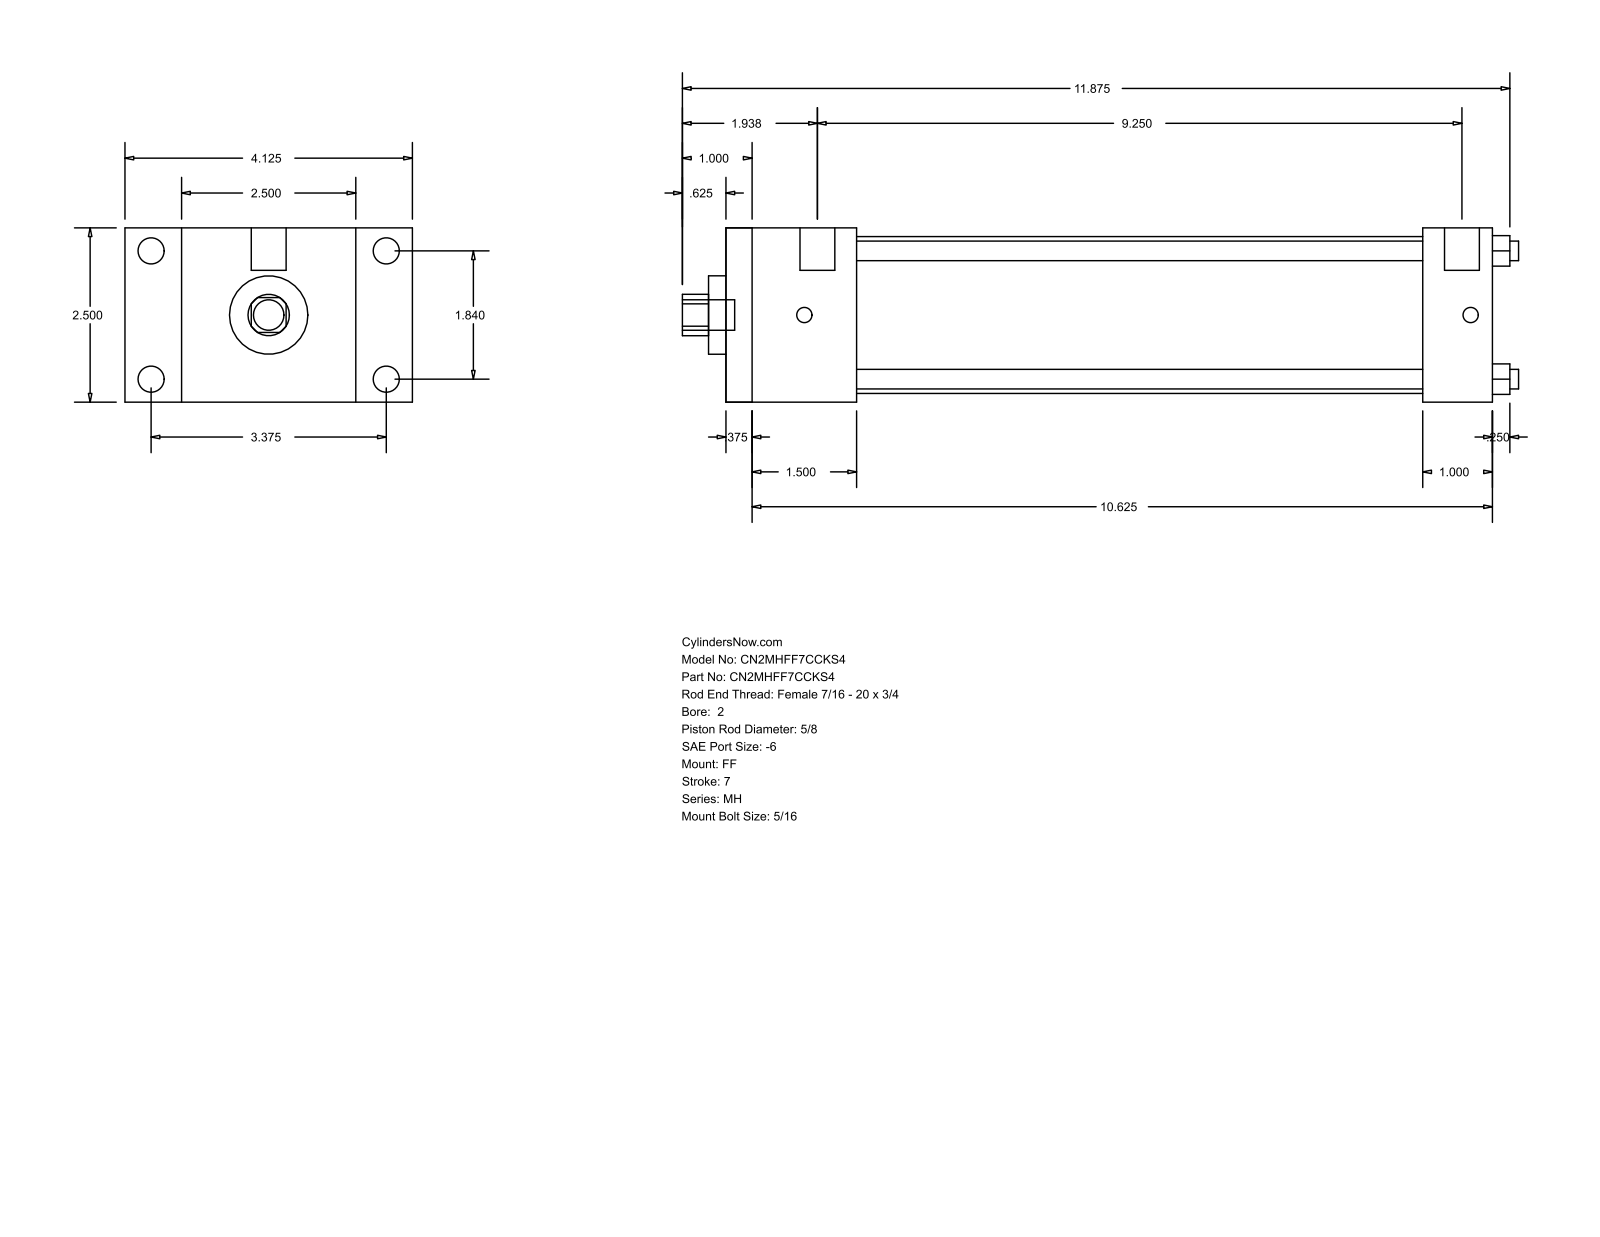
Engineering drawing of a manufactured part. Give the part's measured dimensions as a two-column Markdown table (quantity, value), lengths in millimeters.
| quantity | value |
| --- | --- |
| part name | MH_FF__0200_0.625 |
| STEP written by | GSSL Pune (CONFIG_CONTROL_DESIGN) |
| units | millimeters |
| bodies | 0 solids, 92 faces (64 planar, 28 cylindrical, 0 other) |
| overall size | 304.8 × 104.78 × 63.5 |
| round holes (diameter × count) | 7.14 × 4, 15.88 × 1, 28.57 × 1, 57.15 × 1 |
| round bosses / shafts (diameter × count) | 9.53 × 4, 5.56 × 4, 12.7 × 2, 11.11 × 1 |
| partial cylindrical surfaces (radius × count) | 7.54 × 1 |
| main face-to-face distances | 63.5, 279.39, 9.52, 269.87, 38.1, 47.62, 254, 244.48, 206.38, 231.77 |
| hole center spacings | 33.05, 46.74, 66.1 |
